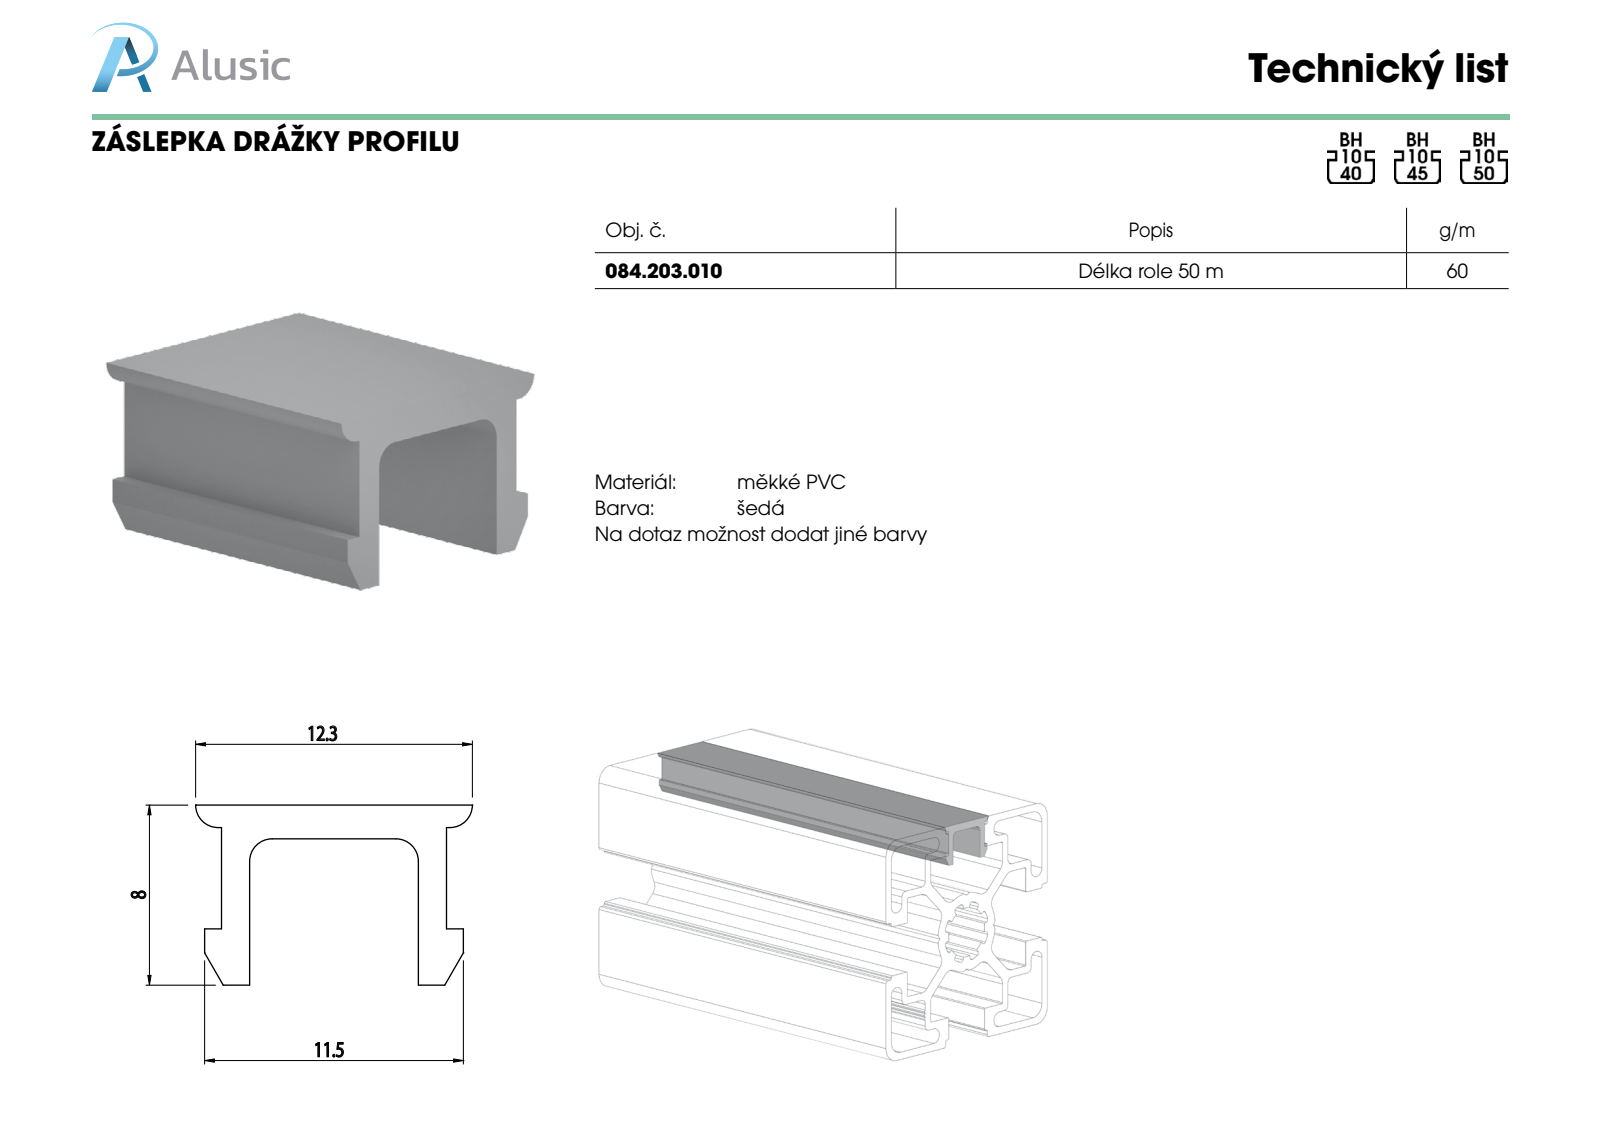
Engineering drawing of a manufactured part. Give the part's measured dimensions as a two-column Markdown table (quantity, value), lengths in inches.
| quantity | value |
| --- | --- |
| part name | 084.203.010 |
| STEP written by | SolidWorks 2011 (CONFIG_CONTROL_DESIGN) |
| units | inches |
| bodies | 1 solid, 22 faces (18 planar, 4 cylindrical, 0 other) |
| overall size | 3.937 × 0.484 × 0.315 |
| volume | 0.22 in³ |
| surface area | 8.43 in² |
| partial cylindrical surfaces (radius × count) | 0.039 × 4 |
| main face-to-face distances | 0.049, 0.344, 0.295, 0.059, 0.394, 0.256, 0.315, 0.03, 0.079, 0.374 |
